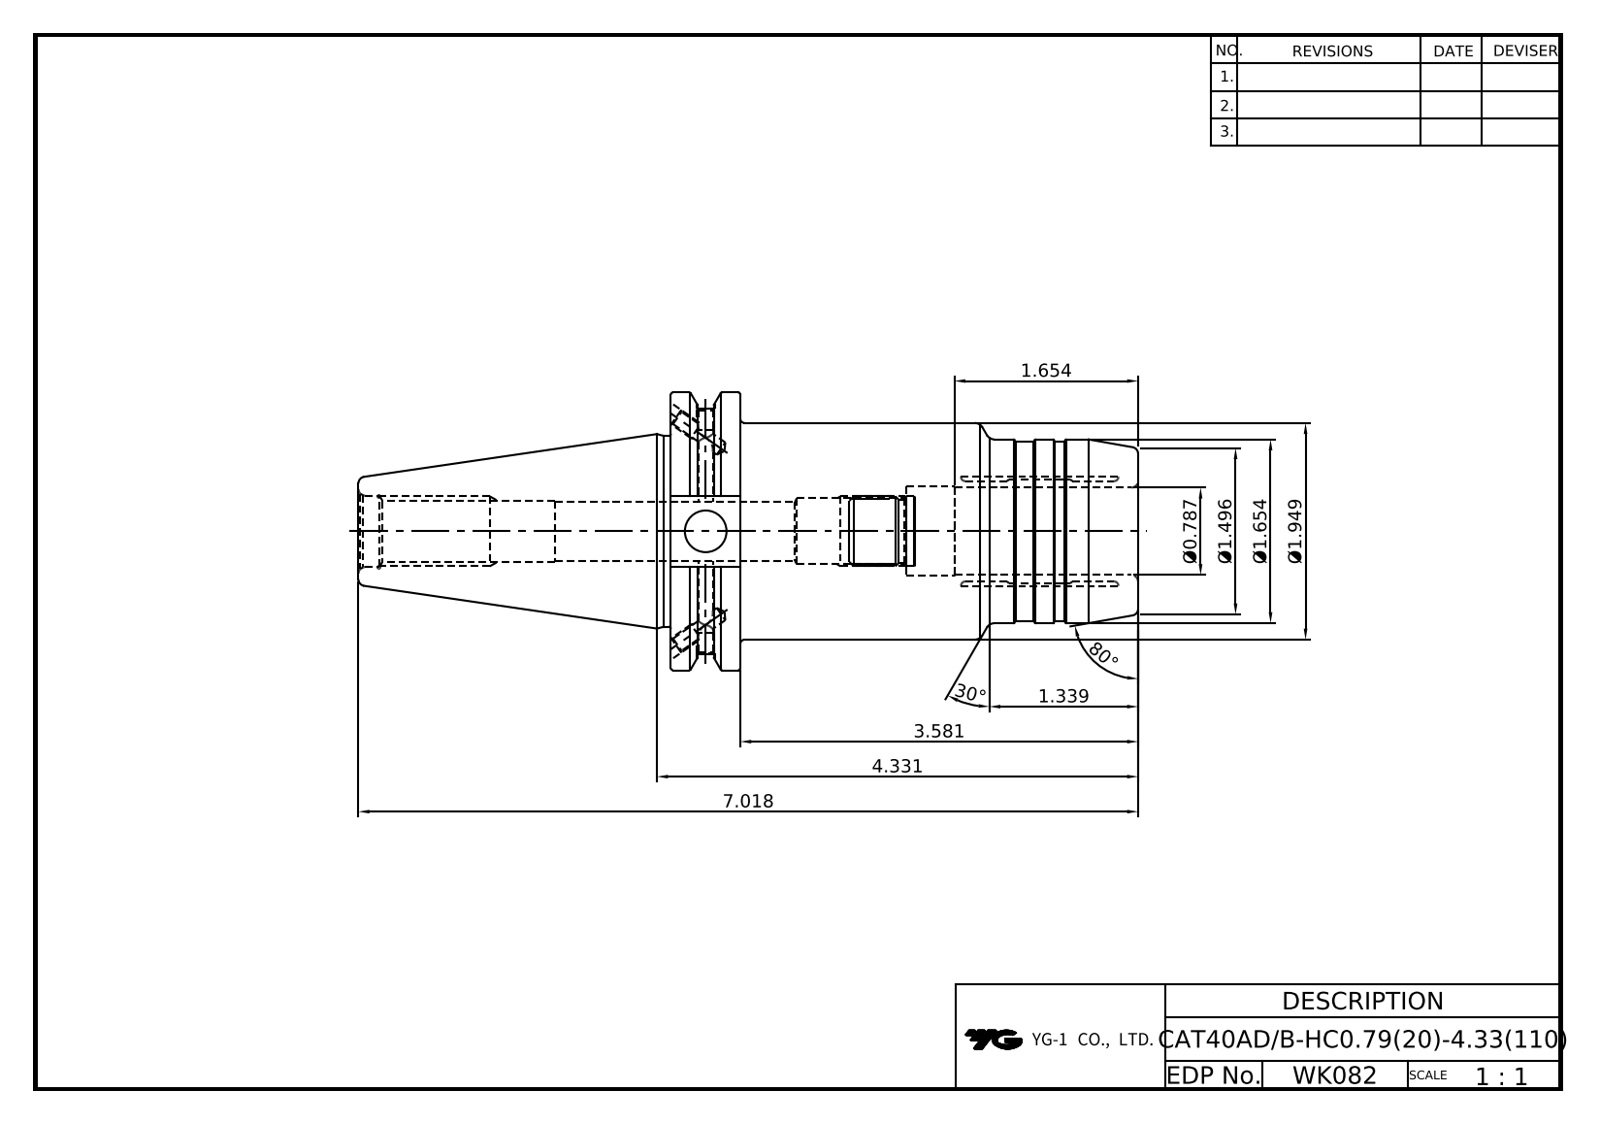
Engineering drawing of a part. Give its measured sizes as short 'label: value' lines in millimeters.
name: LO-CAT40ADB-HC20-110
written by: Autodesk Inventor 2020 (AUTOMOTIVE_DESIGN)
unit: mm
bodies: 1 solid, 106 faces (34 planar, 35 cylindrical, 37 other)
size: 178.25 × 63.5 × 61.09
volume: 231 949 mm³; area: 38 480 mm²
holes: 4× ⌀3.24, 2× ⌀4, 2× ⌀4.2, 1× ⌀9.53, 1× ⌀13, 1× ⌀13.39, 1× ⌀14.92, 1× ⌀16.3, 1× ⌀20, 1× ⌀20.4
bosses: 1× ⌀63.5, 1× ⌀49.5, 1× ⌀43.6, 1× ⌀42, 1× ⌀41
rounds: 1× R8.19, 1× R28.15
face distances: 15.88, 106.83, 90.95, 47.6, 16.38, 53.83, 37.95, 53, 71.42, 87.3
